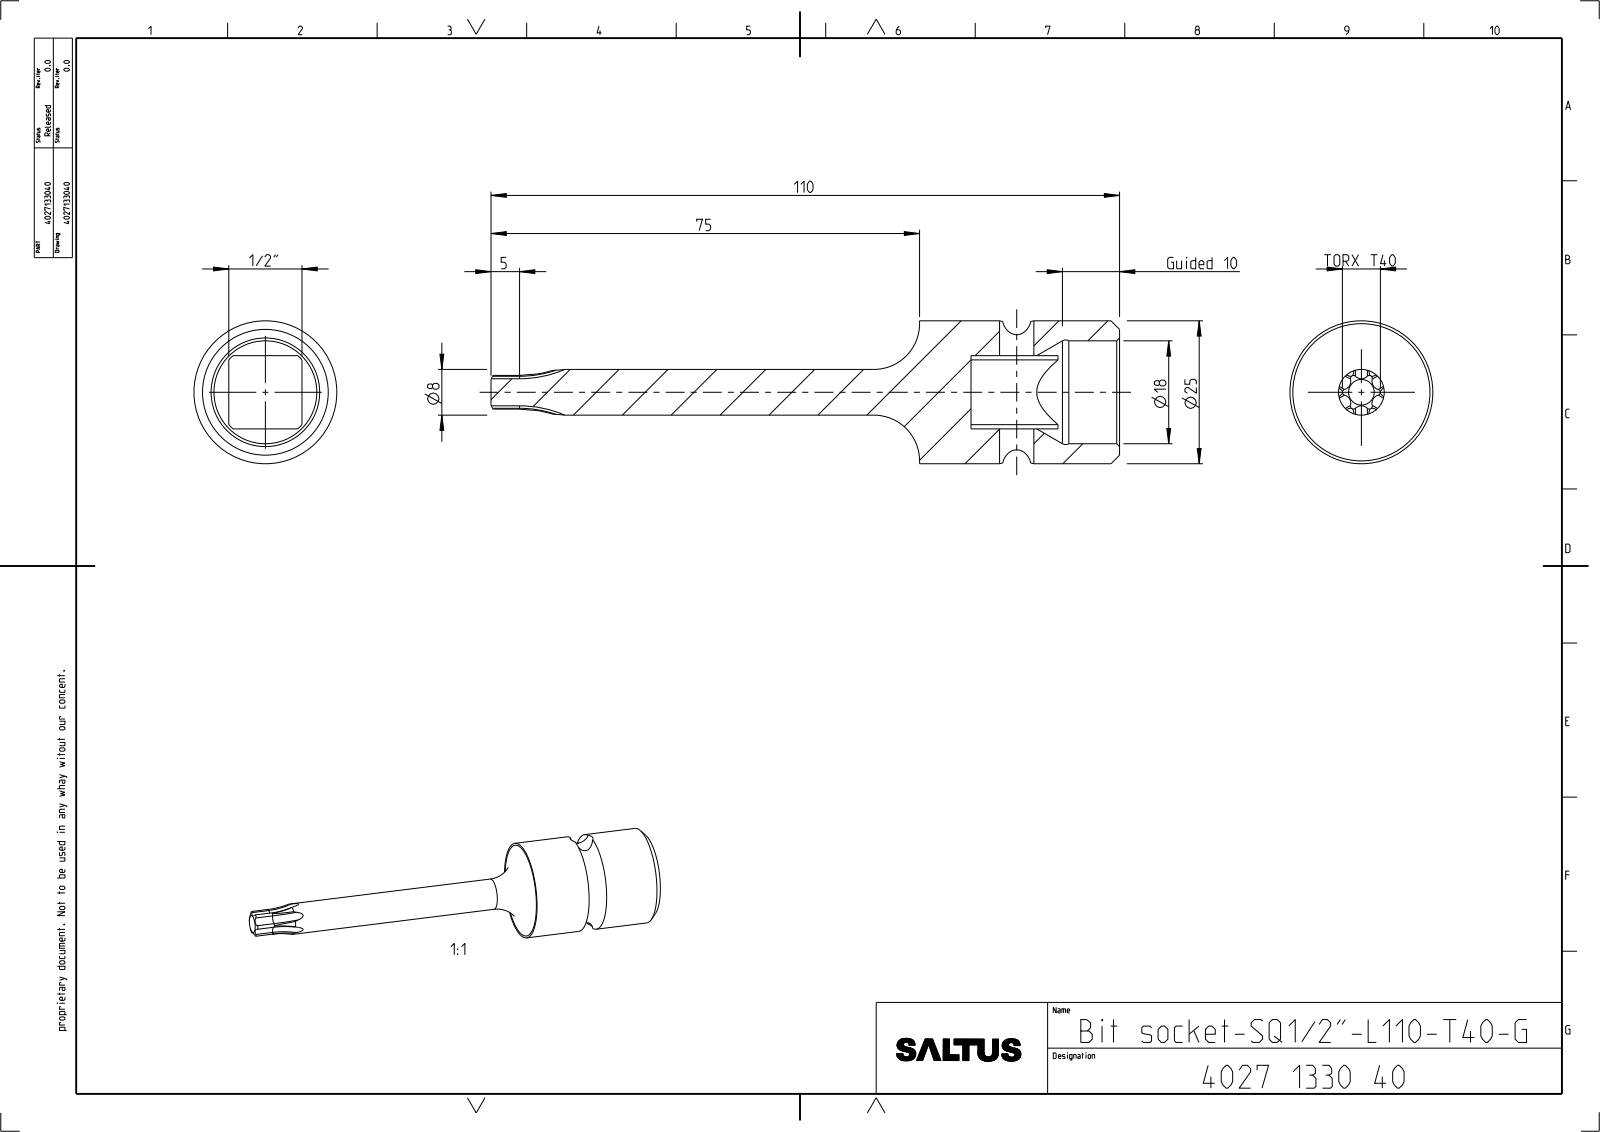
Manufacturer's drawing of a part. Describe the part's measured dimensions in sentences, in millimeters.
The part is named "4027133040". Its 3-D file was written by "CREO PARAMETRIC BY PTC INC, 2022414 (CONFIG_CONTROL_DESIGN)". It is 1 solid with 80 faces: 8 planar, 34 cylindrical and 38 other. Overall it measures 110 by 25 by 25 millimeters. Its volume is 14 989 cubic millimeters and its surface area 6 882 square millimeters. Round holes: 1 of diameter 6, 1 of diameter 18. Round bosses or shafts: 1 of diameter 25, 1 of diameter 8. Partial cylindrical surfaces (rounded edges, fillets, slot ends): 6 of radius 0.51, 6 of radius 1.47, 1 of radius 3.33, 1 of radius 8.55. The main face-to-face distances are 12.82, 26, 35, 9, 110, 84, 75.
